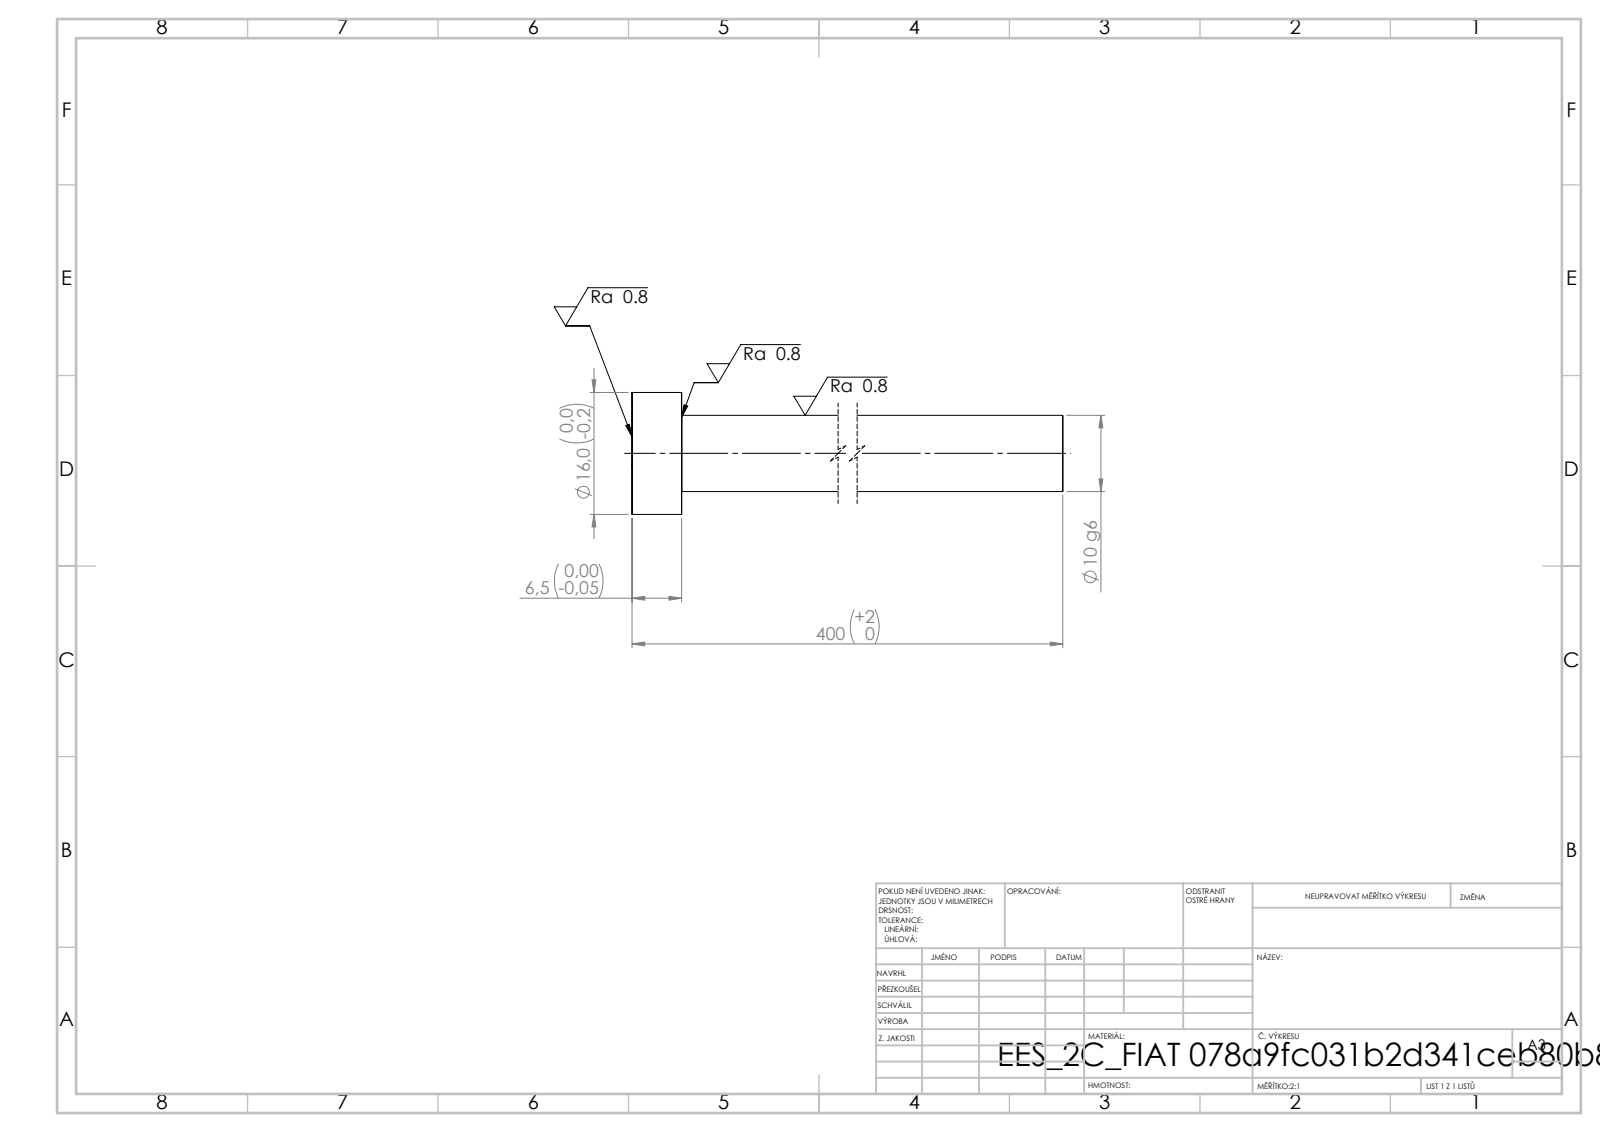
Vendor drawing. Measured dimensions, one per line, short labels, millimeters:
written by: SolidWorks 2019 (CONFIG_CONTROL_DESIGN)
unit: mm
bodies: 1 solid, 7 faces (3 planar, 4 cylindrical, 0 other)
size: 400 × 16 × 16
volume: 32 212 mm³; area: 13 091 mm²
bosses: 1× ⌀16, 1× ⌀10
face distances: 6.5, 400, 393.5
